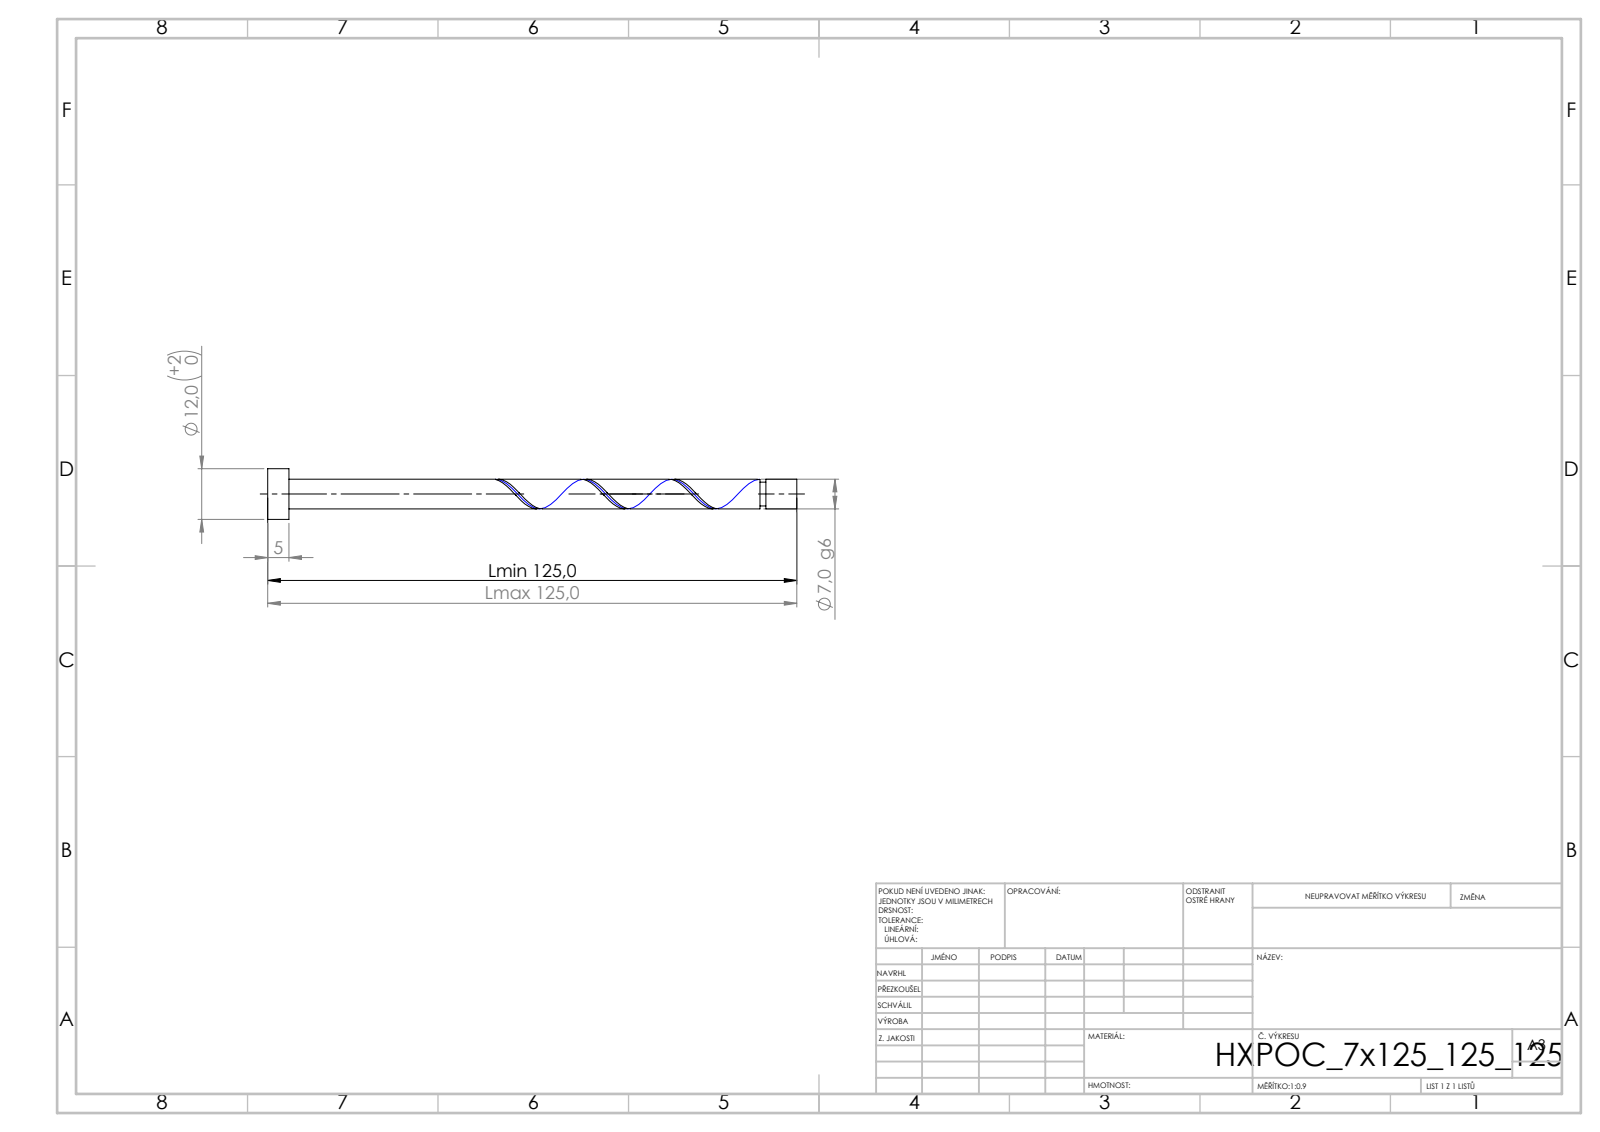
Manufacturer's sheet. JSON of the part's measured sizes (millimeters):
{"step_written_by": "SolidWorks 2019 (CONFIG_CONTROL_DESIGN)", "units": "millimeters", "bodies": {"solids": 1, "faces": 21, "planar": 6, "cylindrical": 14, "other": 1}, "overall_size": [125, 12, 12], "volume_mm3": 5118, "surface_area_mm2": 3145, "round_bosses_or_shafts": [[12, 1], [7, 1], [5.6, 1]], "face_to_face_distances": [5, 125, 120, 117.69, 112.69, 7.31, 116.29, 111.29, 1.4, 8.71]}
